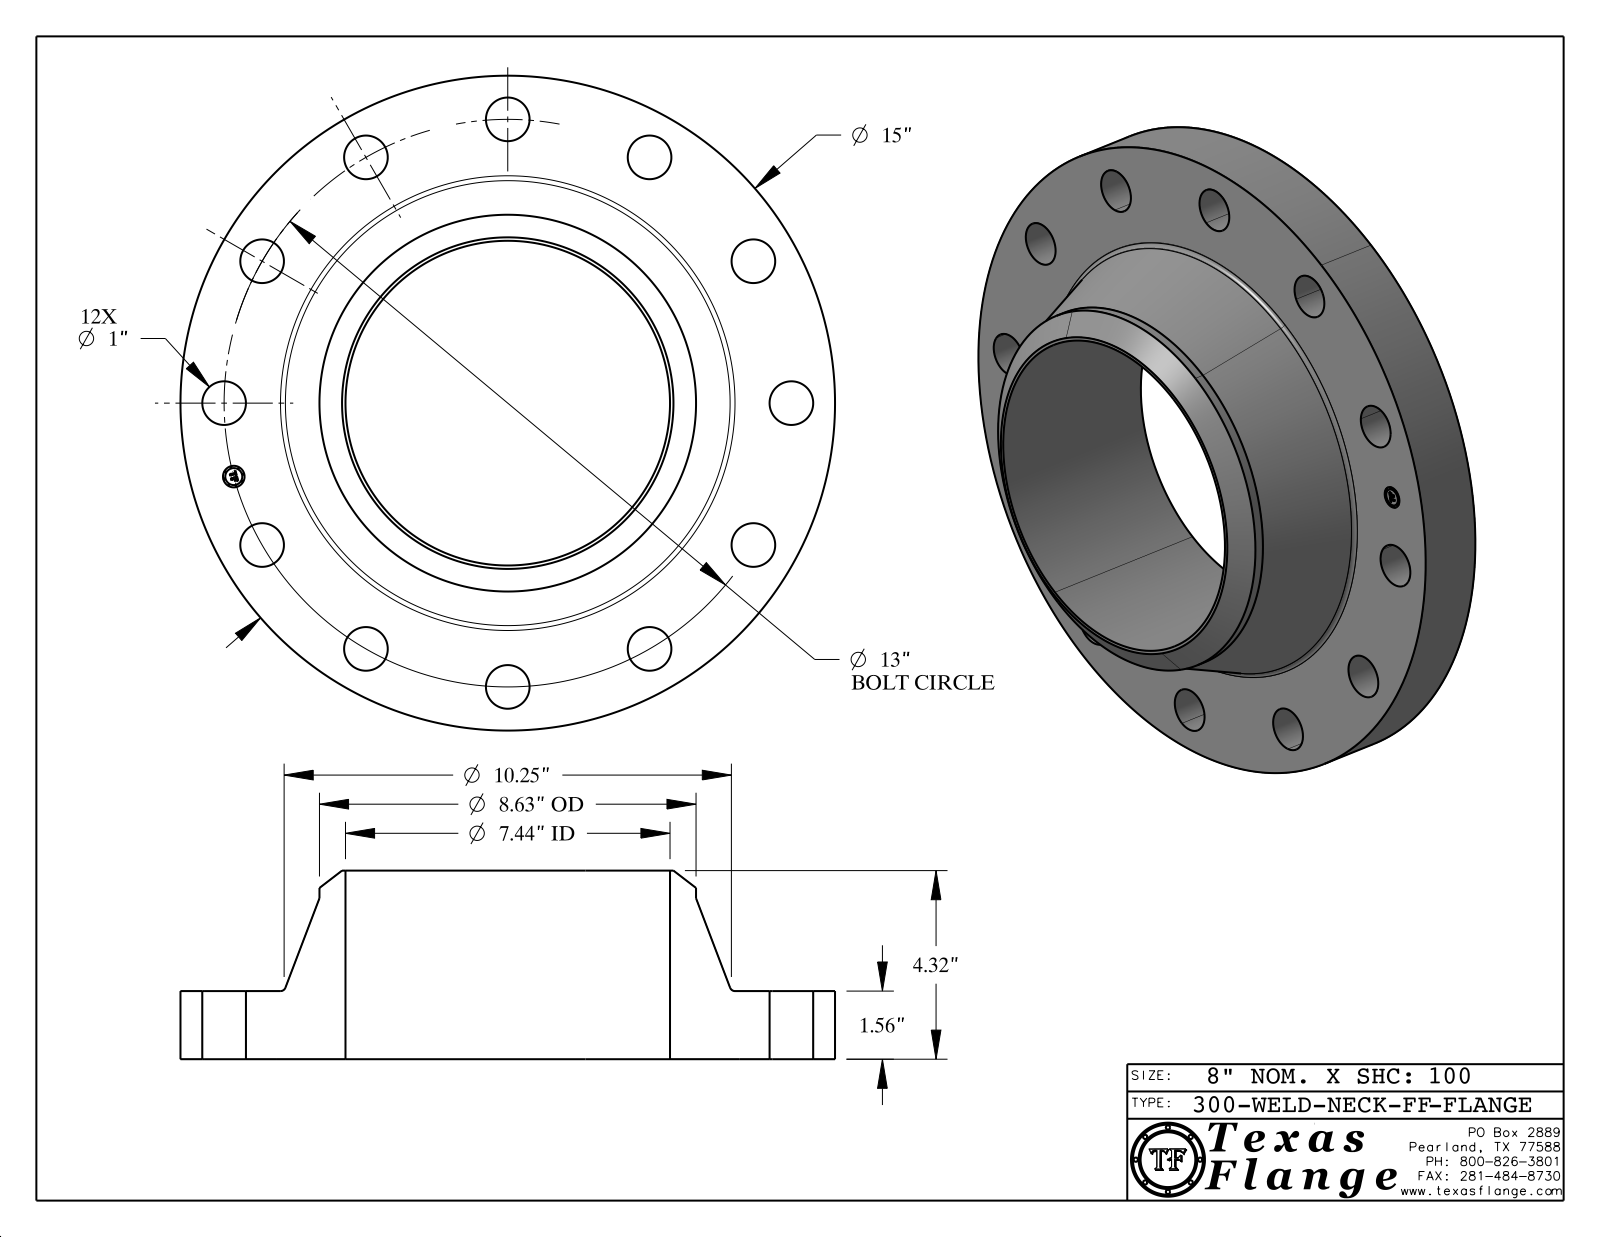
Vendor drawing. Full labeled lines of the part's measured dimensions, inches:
Part name (STEP PRODUCT): 300-WELD-NECK-FF
STEP written by: CATIA V5 STEP AP214 (AUTOMOTIVE_DESIGN)
Units: inches
Bodies: 1 solid, 425 faces (369 planar, 50 cylindrical, 6 other)
Overall size (bounding box): 15 × 15 × 4.32
Volume: 256.9 in³ · Surface area: 533.7 in²
Round holes (diameter × count): ⌀1 ×12, ⌀0.495 ×1, ⌀7.437 ×1
Round bosses / shafts (diameter × count): ⌀0.03 ×8, ⌀15 ×1, ⌀8.63 ×1, ⌀0.39 ×1
Main face-to-face distances: 1.56, 4.32, 2.76, 1.545, 0.015, 2.775, 0.148, 0.144, 0.027, 0.096
Hole centre spacings: 6.5, 3.365, 9.193, 11.258, 12.557, 13, 1.697, 4.975
